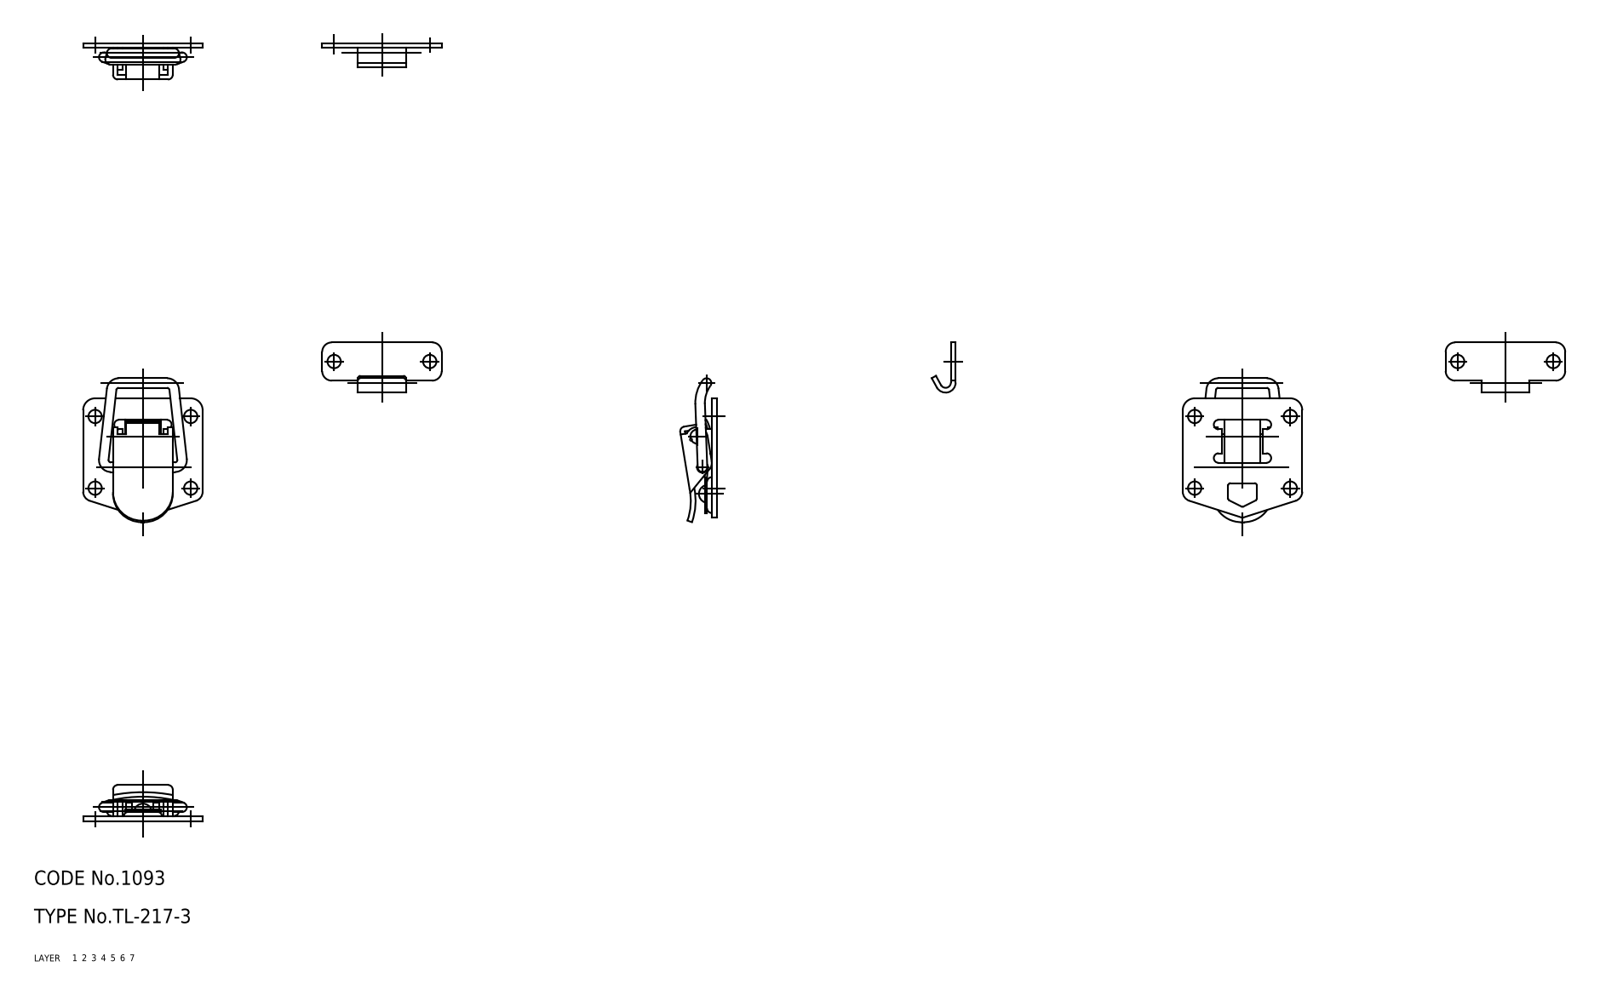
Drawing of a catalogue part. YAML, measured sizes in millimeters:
part_name: "shaft; rivet; lever; leaf spring (+4 more)"
step_written_by: "CADfix (AUTOMOTIVE_DESIGN)"
units: millimeters
bodies: {solids: 7, faces: 196, planar: 0, cylindrical: 0, other: 196}
overall_size: [37.62, 25, 7.61]
volume: 1380
surface_area: 3370
